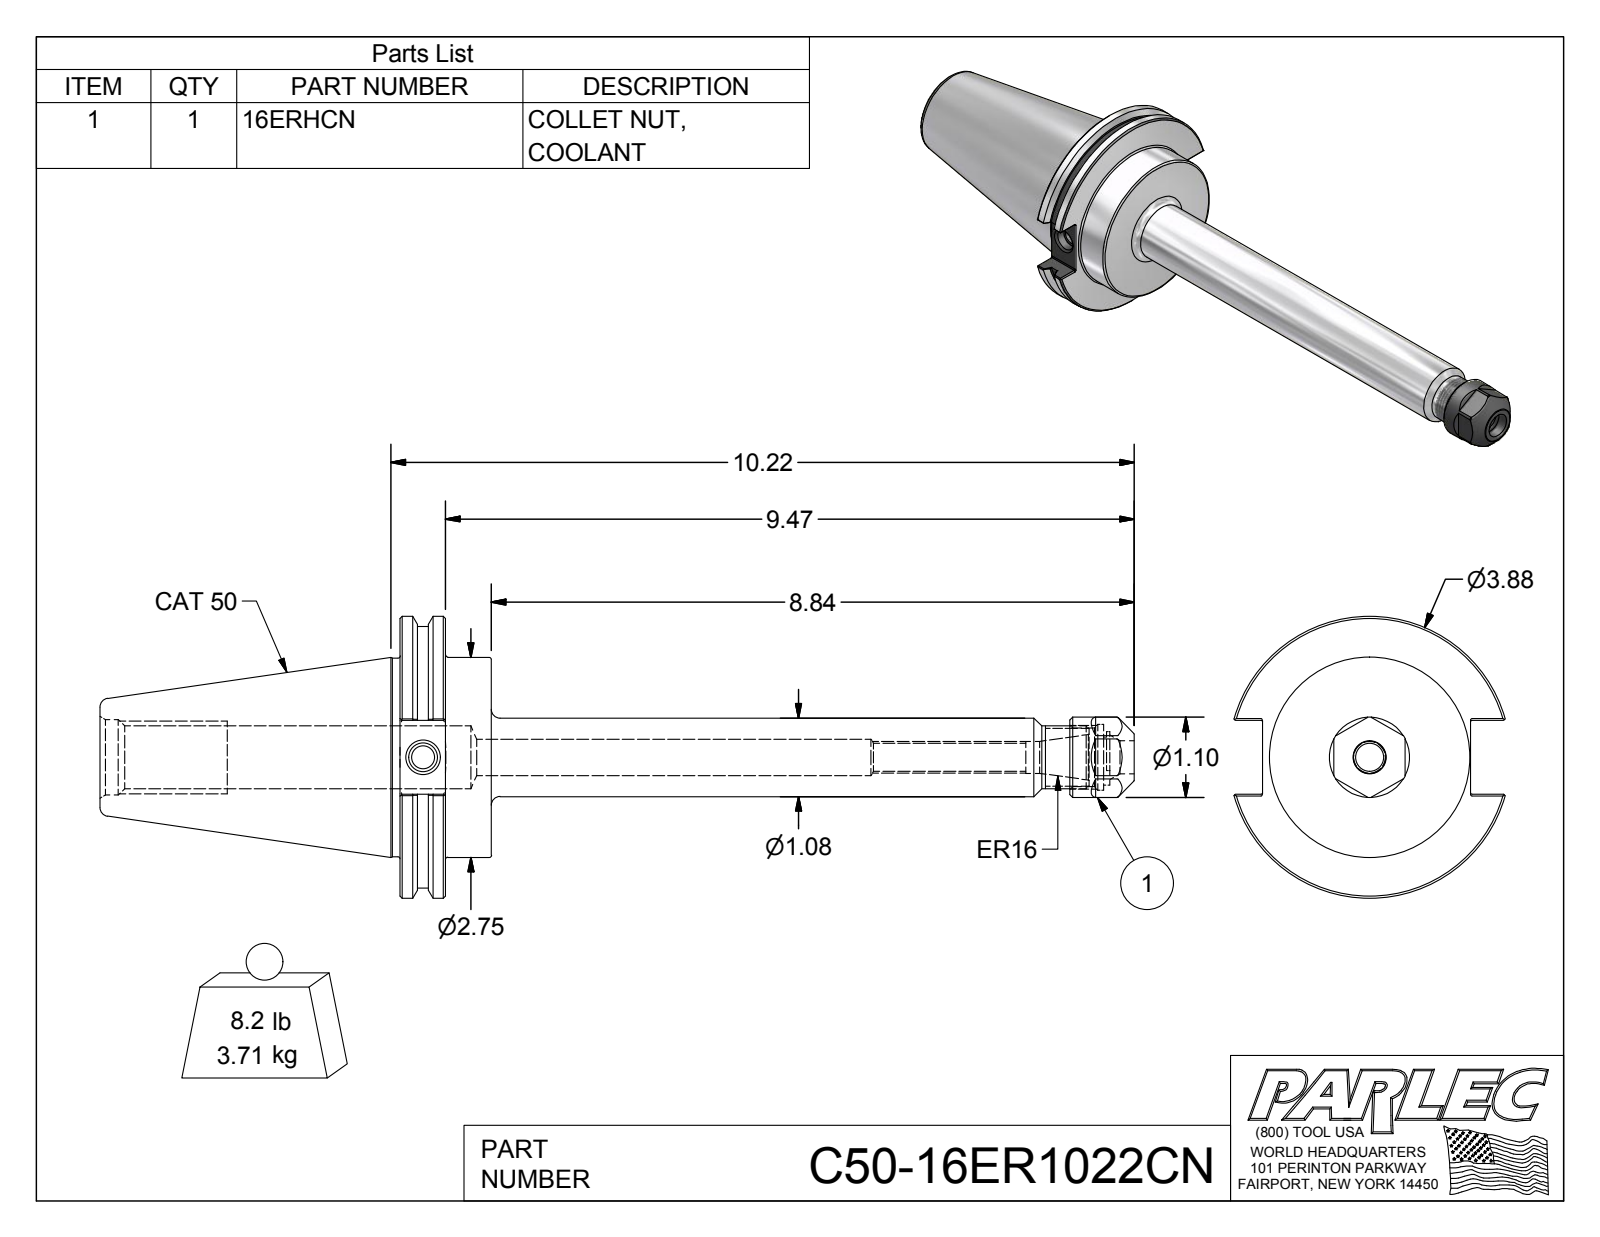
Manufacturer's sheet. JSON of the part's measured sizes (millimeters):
{"part_name": "C50-16ER1022CN; C50-16ER10-1; 16ERHCN", "step_written_by": "Autodesk Inventor 2012 (AUTOMOTIVE_DESIGN)", "units": "millimeters", "bodies": {"solids": 2, "faces": 130, "planar": 50, "cylindrical": 35, "other": 45}, "overall_size": [361.2, 98.4, 94.7], "volume_mm3": 476200, "surface_area_mm2": 77740, "round_holes": [[8, 1], [9.7, 1], [10.1, 1], [11.2, 1], [11.5, 1], [12.7, 1], [16.8, 1], [20.5, 1], [22, 1], [23, 1], [26.4, 1]], "round_bosses_or_shafts": [[98.4, 1], [91.3, 1], [69.9, 1], [69.3, 1], [28, 1], [27.4, 1], [22, 1]], "partial_cylinders_radius": [[0.5, 12], [9, 1]], "face_to_face_distances": [31.9, 15.9, 16, 24.9, 104.8, 120.7, 136.7, 72.6, 25.8, 22], "hole_center_spacings": [1.3]}
